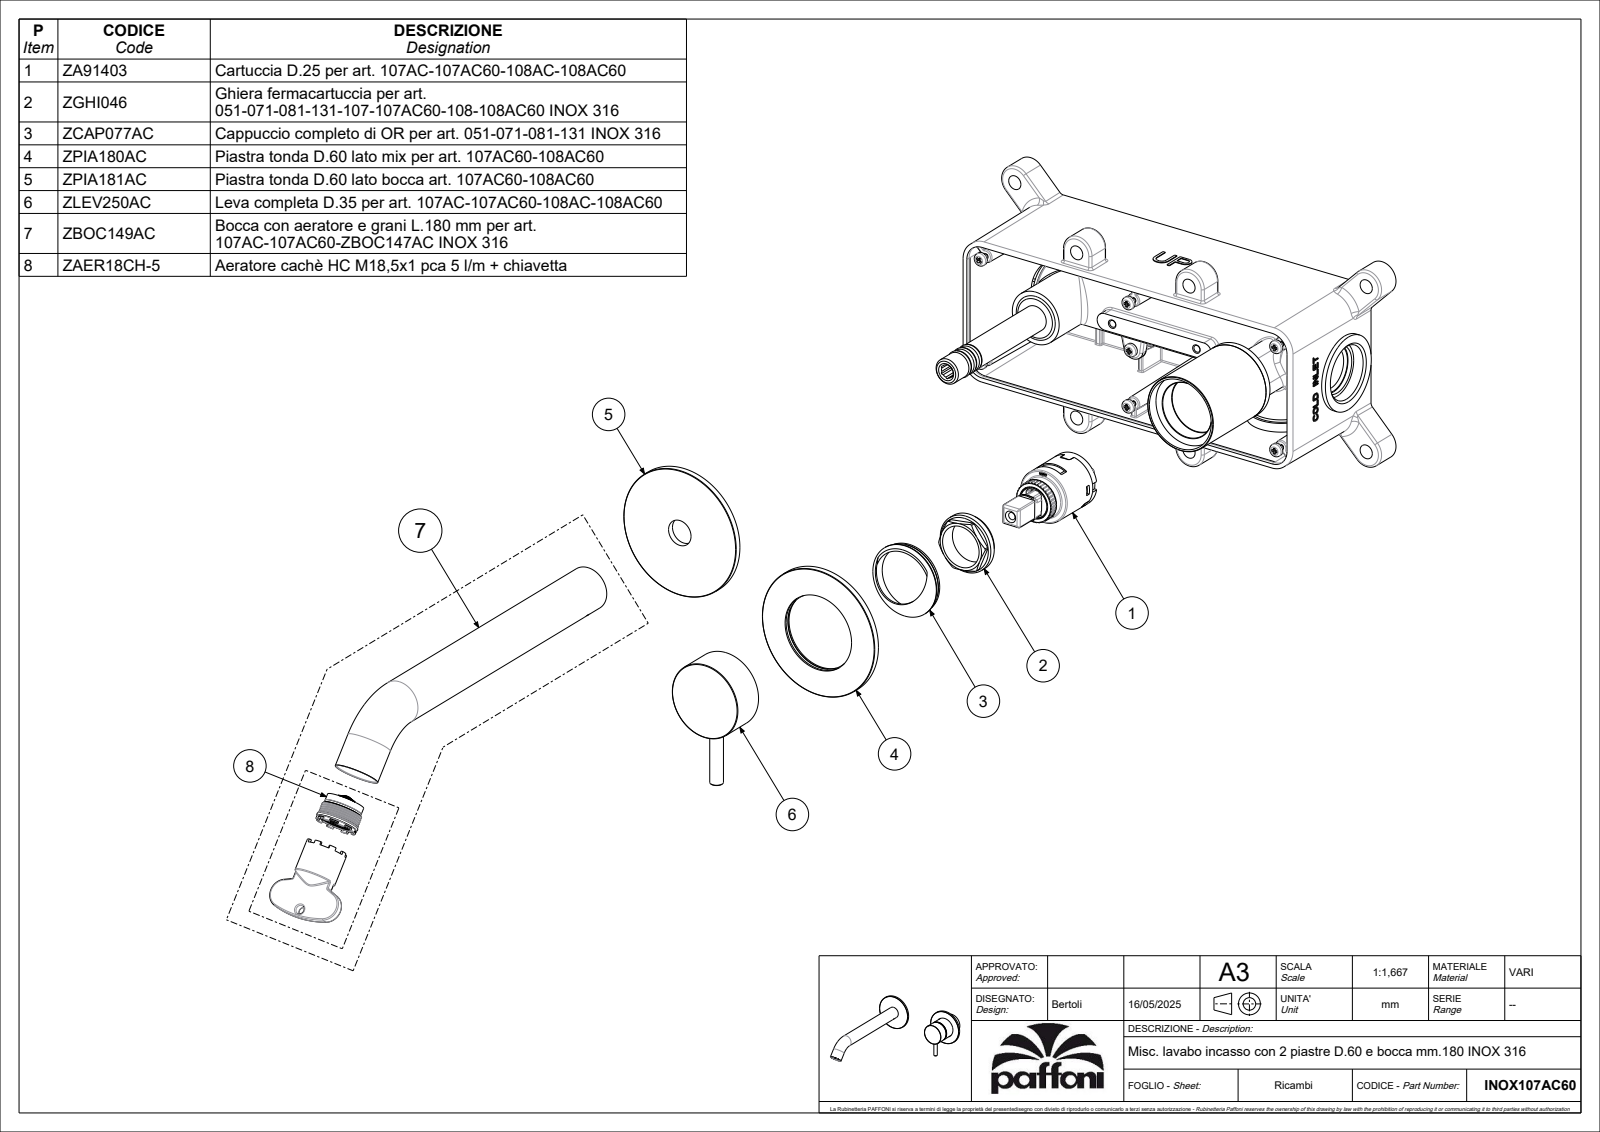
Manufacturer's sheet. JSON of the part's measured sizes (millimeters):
{"part_name": "5010068AC_B_AF1; 4111614_AF1; 4111615AC_AF1; 4111575 (+8 more)", "step_written_by": "CREO PARAMETRIC BY PTC INC, 2022124 (CONFIG_CONTROL_DESIGN)", "units": "millimeters", "bodies": {"solids": 23, "faces": 5075, "planar": 3616, "cylindrical": 1062, "other": 397}, "overall_size": [187.25, 169, 72.7], "volume_mm3": 66553, "surface_area_mm2": 63756, "round_holes": [[4.1, 2], [6.2, 2], [15, 2], [50, 2], [2.98, 1], [3.4, 1], [4, 1], [5.2, 1], [12, 1], [12.7, 1], [13.8, 1], [14, 1]], "round_bosses_or_shafts": [[0.8, 6], [5, 4], [4.5, 3], [60, 2], [45.2, 2], [20, 2], [35, 1], [33.9, 1]], "partial_cylinders_radius": [[0.2, 104], [0.12, 93], [0.15, 34], [1, 15], [0.5, 9], [0.7, 4], [1.5, 4], [2, 2]], "face_to_face_distances": [3, 2, 37.6, 39.6, 36.6, 1, 35.6, 34.6, 2.2, 10.6], "hole_center_spacings": [109]}
